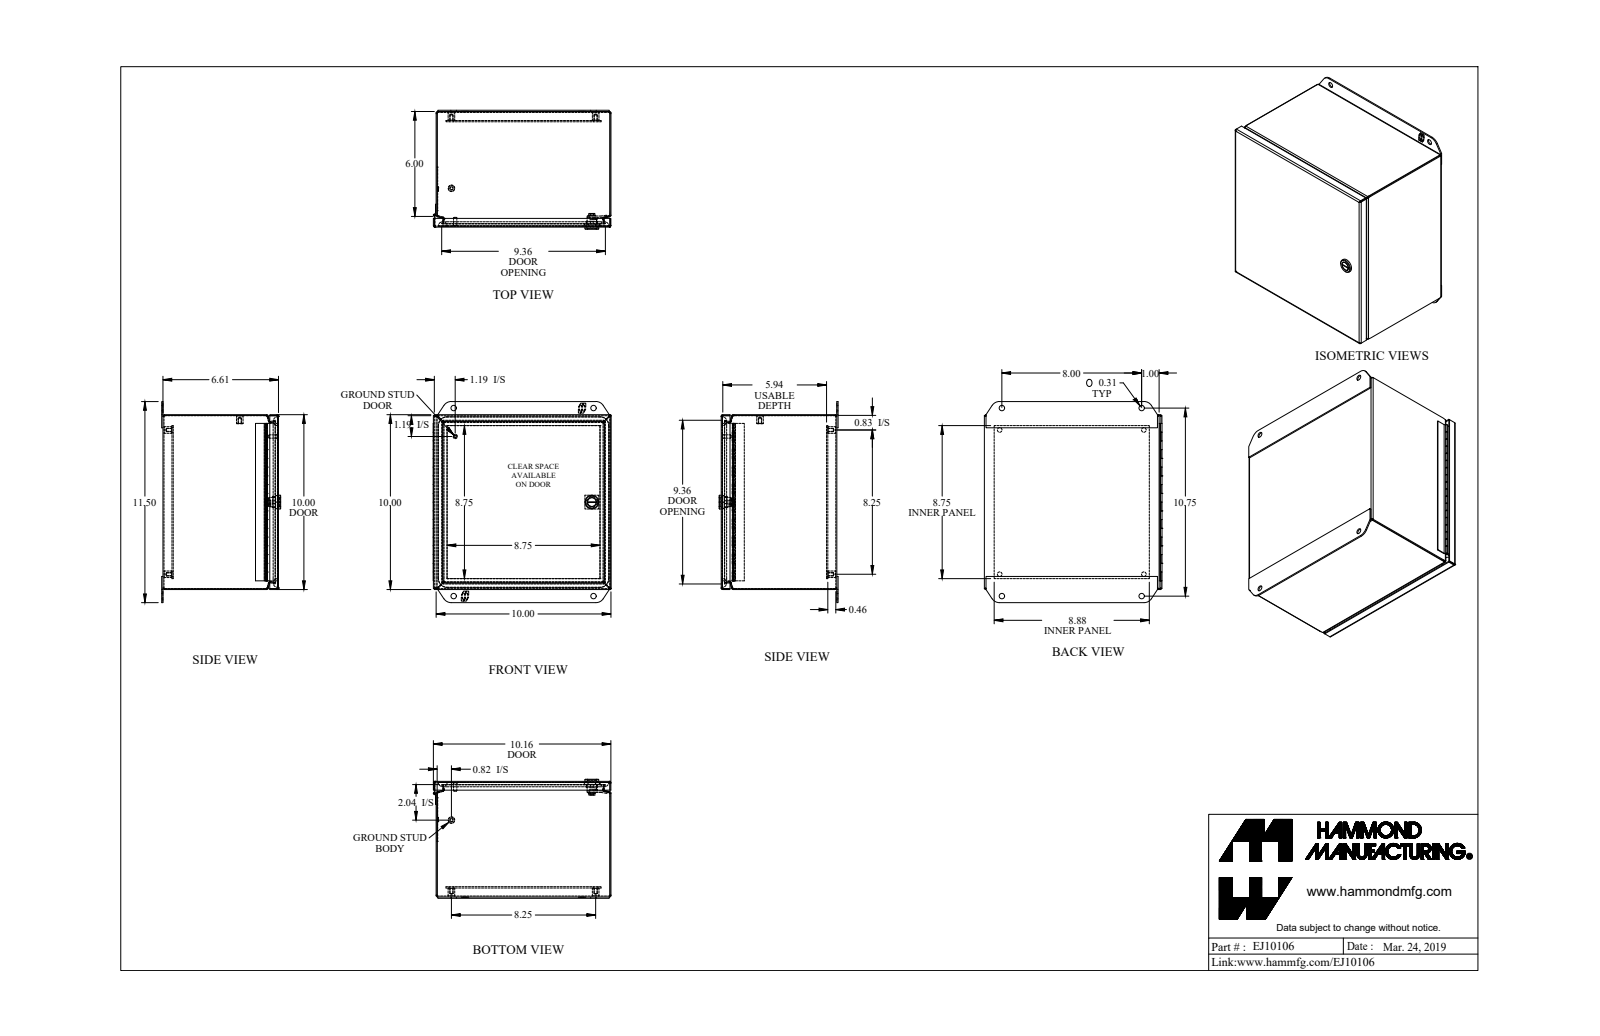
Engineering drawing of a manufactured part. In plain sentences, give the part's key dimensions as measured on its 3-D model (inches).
The part is named "EJ10106_Default". Its 3-D file was written by "SolidWorks 2019 (CONFIG_CONTROL_DESIGN)". It is 16 solids with 675 faces: 377 planar, 206 cylindrical and 92 other. Overall it measures 11.5 by 10.165 by 6.805 inches. Its volume is 39.42 cubic inches and its surface area 1 304 square inches. Round holes: 5 of diameter 0.156, 4 of diameter 0.265, 4 of diameter 0.313, 1 of diameter 0.05, 1 of diameter 0.516. Round bosses or shafts: 5 of diameter 0.375, 1 of diameter 0.788, 1 of diameter 0.535, 1 of diameter 0.496, 1 of diameter 0.435, 1 of diameter 0.25, 1 of diameter 0.188, 1 of diameter 0.1. Partial cylindrical surfaces (rounded edges, fillets, slot ends): 16 of radius 0.029, 16 of radius 0.086, 10 of radius 0.281, 4 of radius 0.25, 4 of radius 0.499, 4 of radius 0.5, 2 of radius 0.06, 2 of radius 0.539. The main face-to-face distances are 0.057, 9.943, 6.554, 10, 9.886, 0.072, 0.589, 6.611, 6.497, 0.46. The hole center spacings are 8.25, 1.257, 9.501, 8.22, 12.5, 4.131, 5.376, 8.
